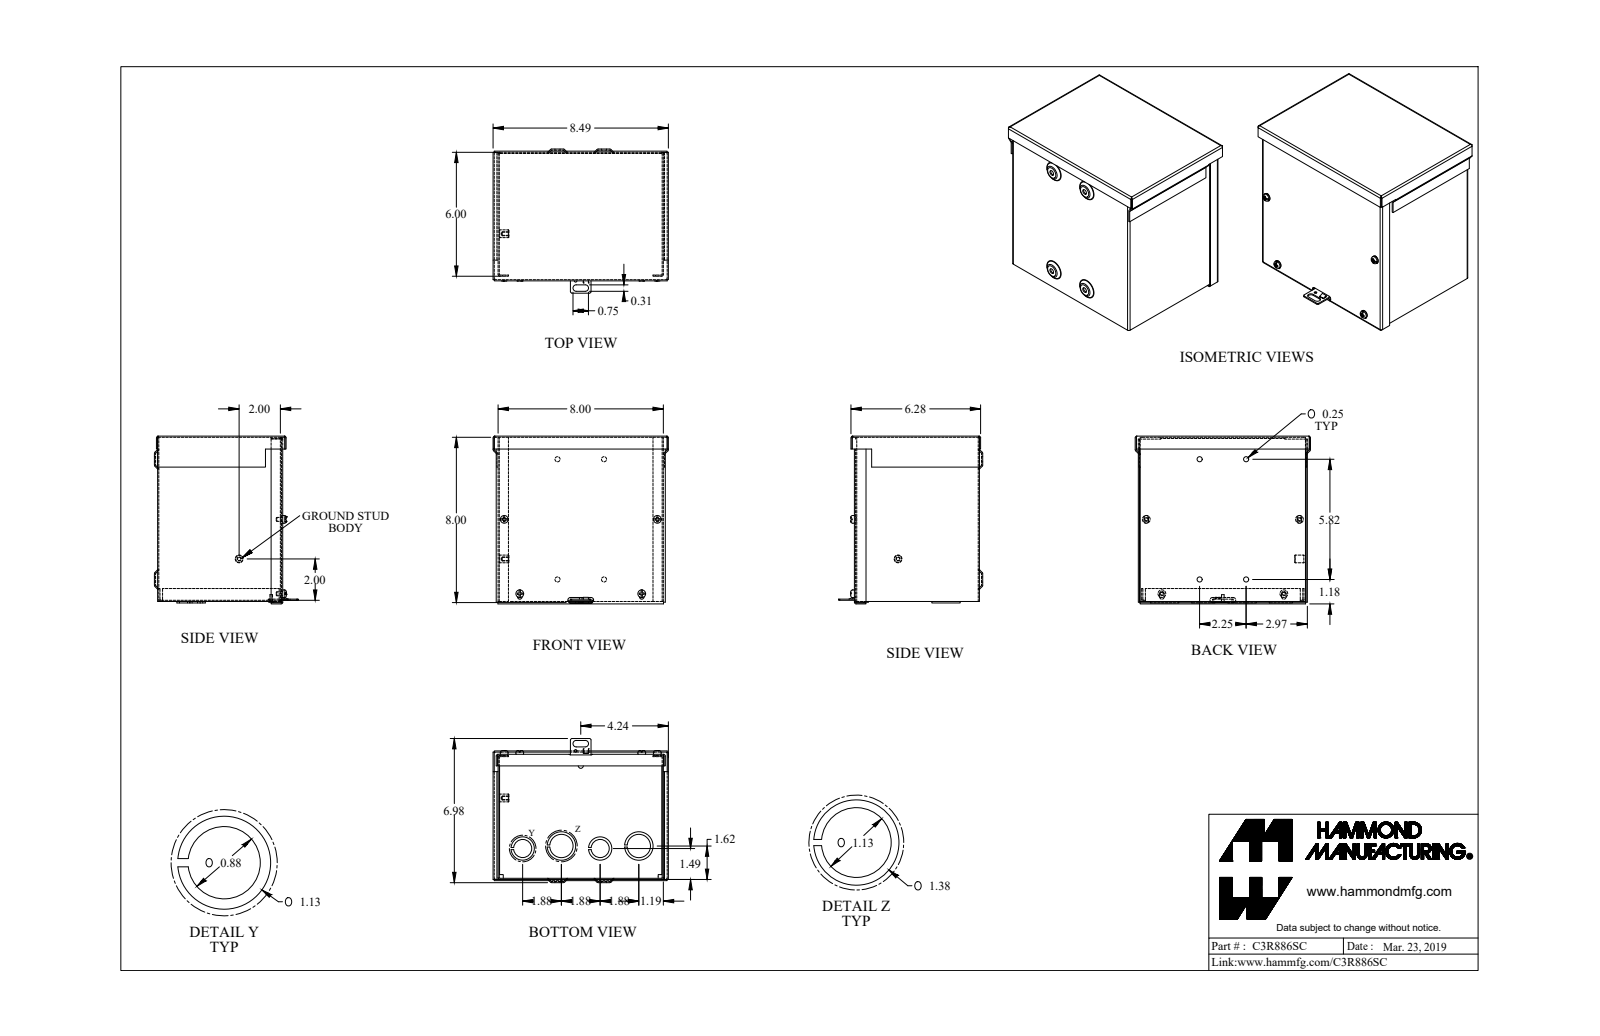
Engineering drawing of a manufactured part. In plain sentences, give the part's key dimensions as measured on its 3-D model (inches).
The part is named "C3R886SC_Default". Its 3-D file was written by "SolidWorks 2019 (CONFIG_CONTROL_DESIGN)". It is 11 solids with 424 faces: 223 planar, 115 cylindrical and 86 other. Overall it measures 8.489 by 8.12 by 6.977 inches. Its volume is 22.11 cubic inches and its surface area 782.9 square inches. Round holes: 4 of diameter 0.17, 4 of diameter 0.25, 1 of diameter 0.125, 1 of diameter 0.137, 1 of diameter 0.156, 1 of diameter 0.875, 1 of diameter 0.875, 1 of diameter 1.125, 1 of diameter 1.125. Round bosses or shafts: 4 of diameter 0.375, 4 of diameter 0.19, 2 of diameter 1.125, 1 of diameter 1.375, 1 of diameter 1.375, 1 of diameter 0.375, 1 of diameter 0.125. Partial cylindrical surfaces (rounded edges, fillets, slot ends): 21 of radius 0.029, 21 of radius 0.086, 8 of radius 0.109, 8 of radius 0.125, 2 of radius 0.156. The main face-to-face distances are 0.057, 7.943, 6, 8, 5.943, 0.057, 6.057, 7.886, 7.886, 7.943. The hole center spacings are 3.89, 5.64, 1.88, 1.998, 2.25, 3.75, 3.752, 4.165.
